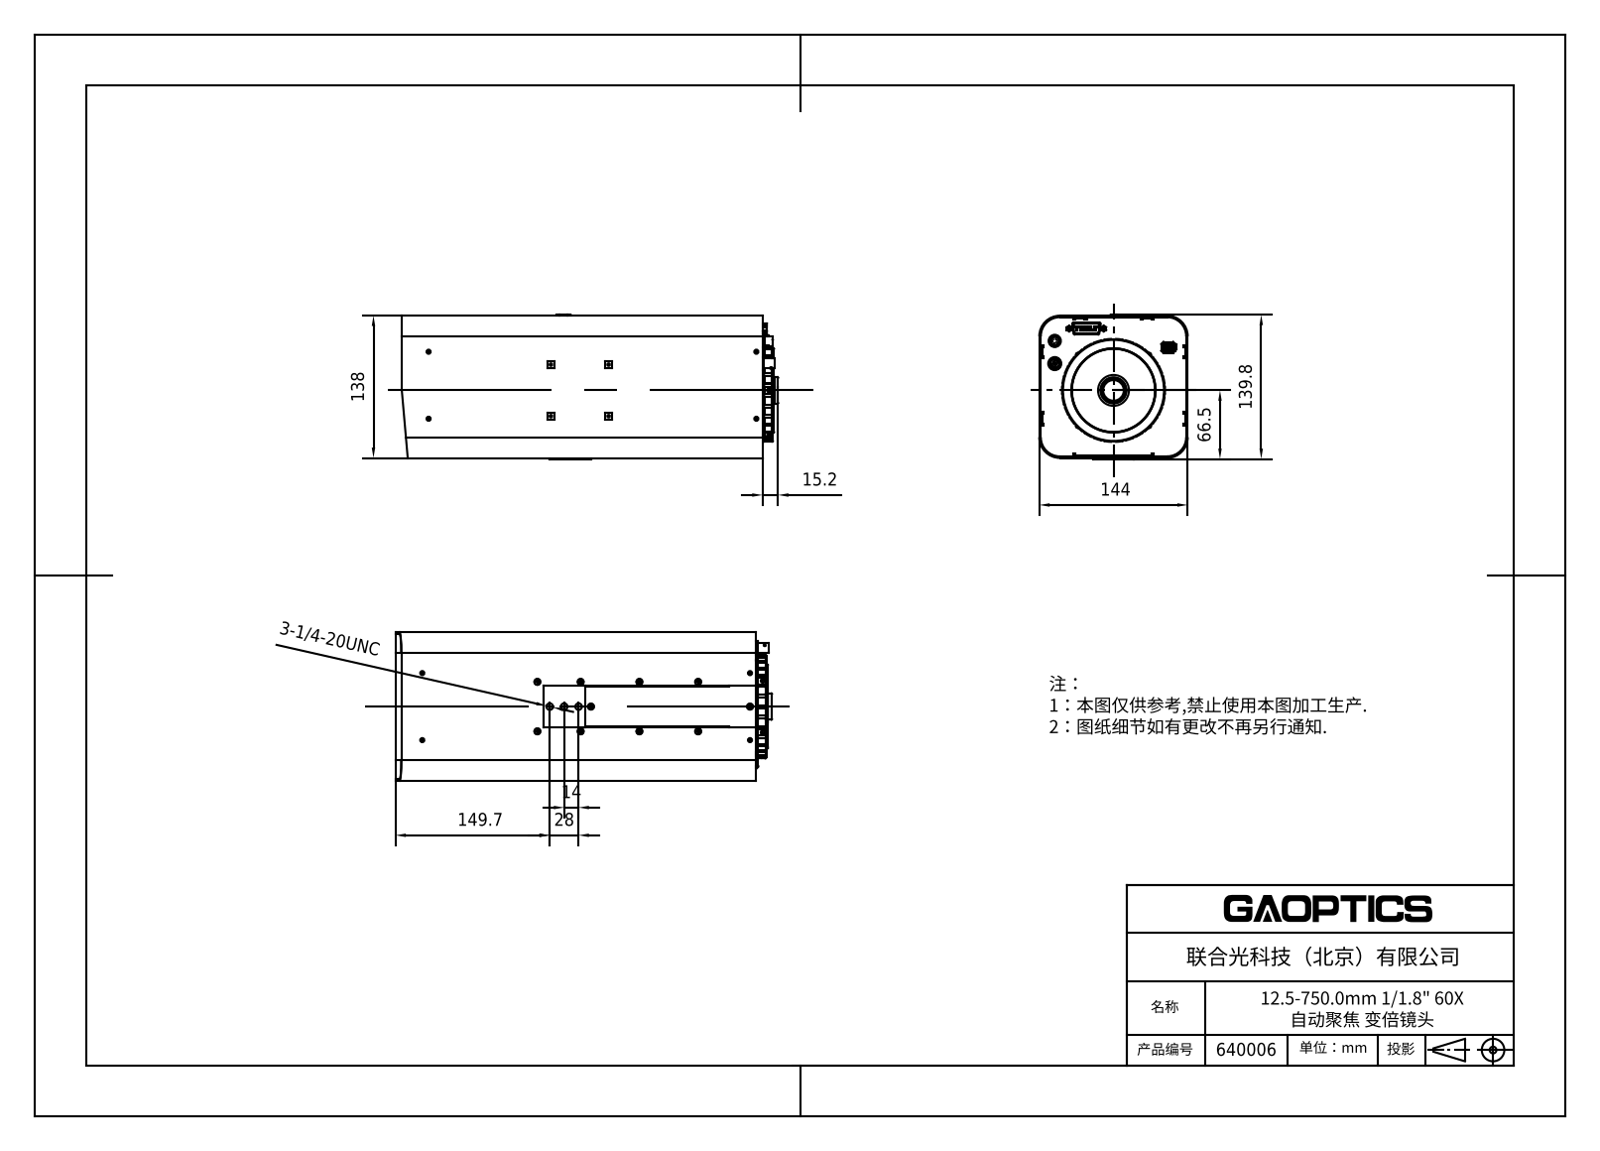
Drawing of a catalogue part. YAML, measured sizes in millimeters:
part_name: "640006"
step_written_by: "SolidWorks 2020 (CONFIG_CONTROL_DESIGN)"
units: millimeters
bodies: {solids: 0, faces: 3072, planar: 1728, cylindrical: 692, other: 652}
overall_size: [365.17, 144, 139.8]
round_holes:
  - {diameter: 3.2, count: 14}
  - {diameter: 2.2, count: 12}
  - {diameter: 3, count: 12}
  - {diameter: 2, count: 11}
  - {diameter: 5.5, count: 4}
  - {diameter: 1.6, count: 3}
  - {diameter: 2.8, count: 3}
  - {diameter: 4, count: 3}
  - {diameter: 6.35, count: 3}
  - {diameter: 8.1, count: 1}
  - {diameter: 9.5, count: 1}
  - {diameter: 20, count: 1}
round_bosses_or_shafts:
  - {diameter: 2, count: 23}
  - {diameter: 3.45, count: 12}
  - {diameter: 5.6, count: 10}
  - {diameter: 3.2, count: 9}
  - {diameter: 3, count: 6}
  - {diameter: 5, count: 4}
  - {diameter: 3.6, count: 4}
  - {diameter: 2.83, count: 4}
partial_cylinders:
  - {radius: 0.5, count: 12}
  - {radius: 1.2, count: 8}
  - {radius: 1.5, count: 8}
  - {radius: 2, count: 8}
  - {radius: 1, count: 6}
  - {radius: 0.2, count: 4}
  - {radius: 0.75, count: 4}
  - {radius: 1.7, count: 4}
face_to_face_distances: [1.5, 136.5, 142.5, 141, 135, 2, 3.5, 144, 138, 134.5]
hole_center_spacings: [26, 14.14, 48, 74.52, 39.29, 48.79, 57, 65]
